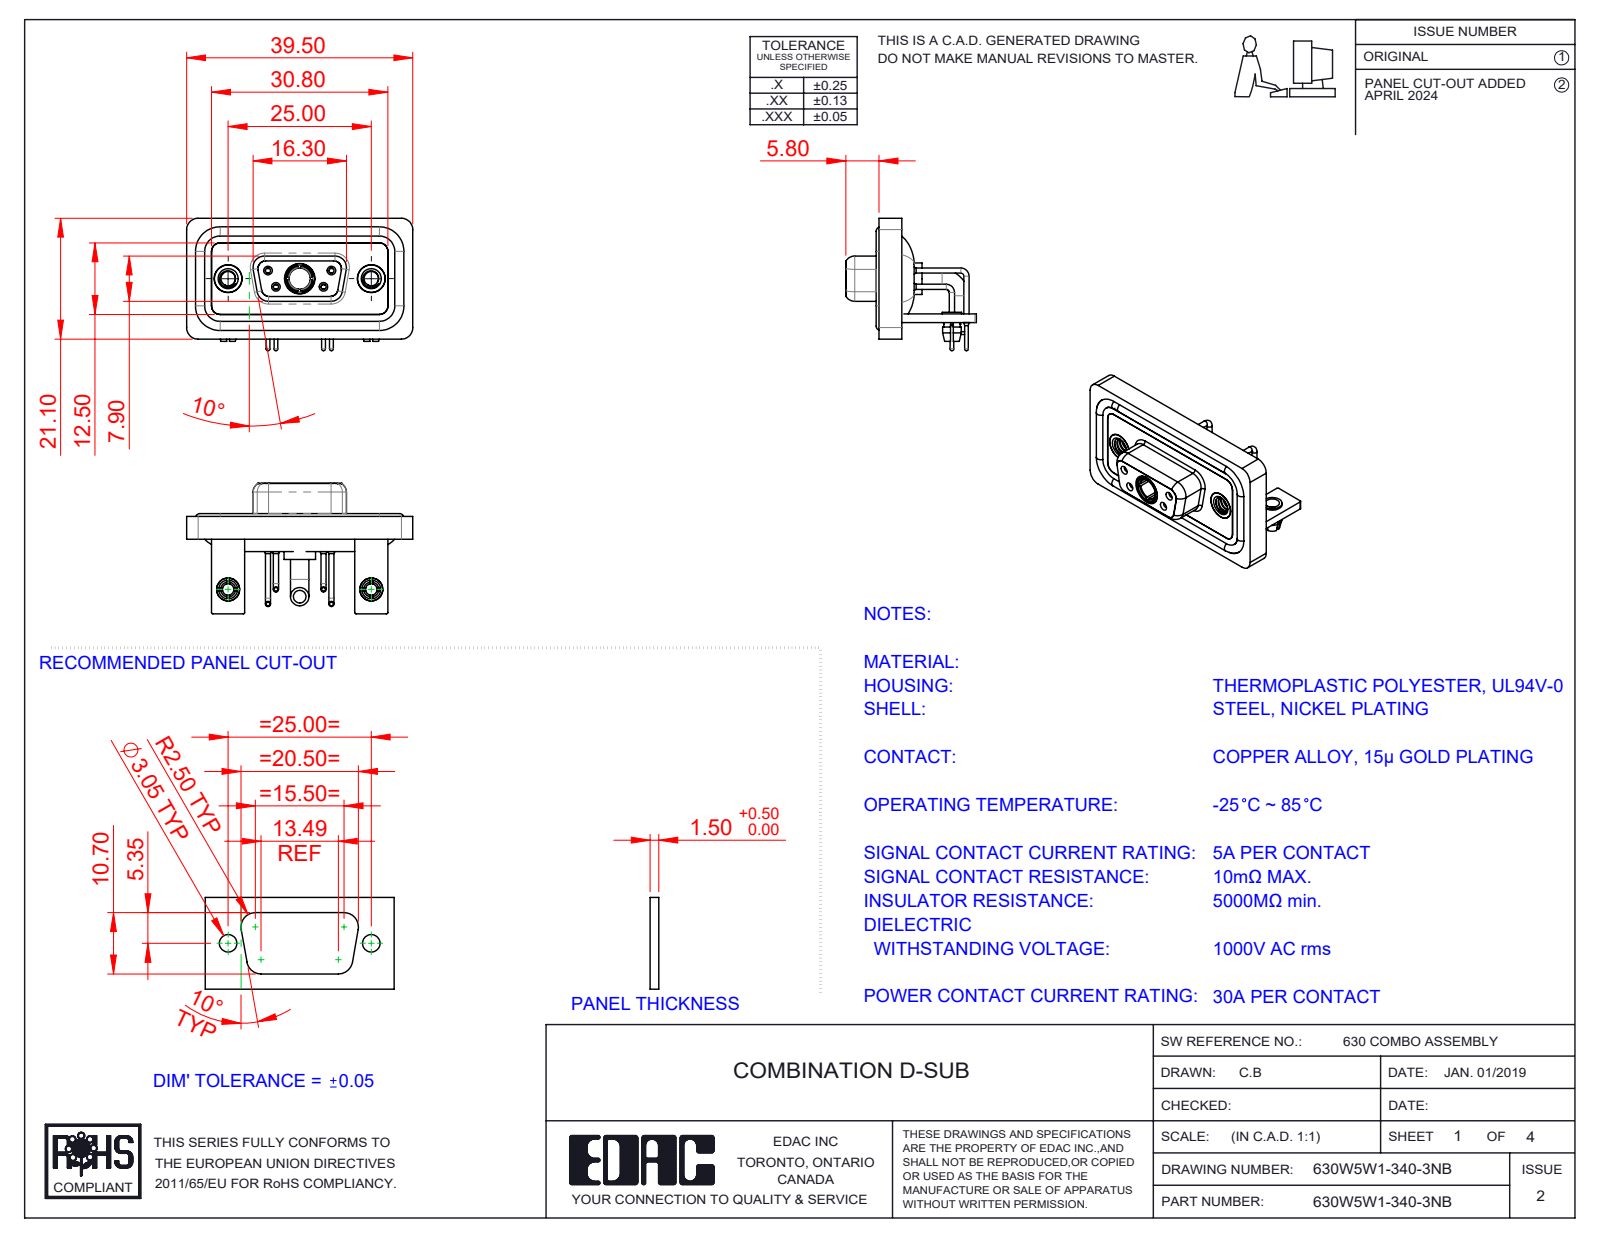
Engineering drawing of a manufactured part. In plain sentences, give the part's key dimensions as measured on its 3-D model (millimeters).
The part is named "630Combo Board Lock_50 Contacts; 630Combo Contact Row 1_50 Contacts; 630Combo Shell Front_09 Contacts; 630Combo Housing_5W1 (+7 more)". Its 3-D file was written by "SolidWorks 2023 (CONFIG_CONTROL_DESIGN)". It is 17 solids with 810 faces: 262 planar, 359 cylindrical and 189 other. Overall it measures 39.5 by 23.12 by 22.8 millimeters. Its volume is 5 252 cubic millimeters and its surface area 8 811 square millimeters. Round holes: 6 of diameter 2, 4 of diameter 0.9, 4 of diameter 1.1, 4 of diameter 1.5, 4 of diameter 2.5, 3 of diameter 4.85, 2 of diameter 1.6, 2 of diameter 1.7, 2 of diameter 3.2, 2 of diameter 4, 2 of diameter 4.05, 2 of diameter 5. Round bosses or shafts: 6 of diameter 1.6, 4 of diameter 0.9, 4 of diameter 0.65, 2 of diameter 4.95, 2 of diameter 4.8, 2 of diameter 4, 2 of diameter 3.4, 2 of diameter 3.3. Partial cylindrical surfaces (rounded edges, fillets, slot ends): 19 of radius 2, 18 of radius 1.5, 16 of radius 0.25, 8 of radius 1.35, 8 of radius 1.6, 5 of radius 0.5, 4 of radius 0.6, 4 of radius 0.65. The main face-to-face distances are 0.4, 2.9, 1.5, 1.8, 1.1, 3.7, 1.6, 0.8, 2.5, 3.1. The hole center spacings are 3.16, 5.72, 7.1, 12.5, 18.1, 25, 4.39, 4.4.
